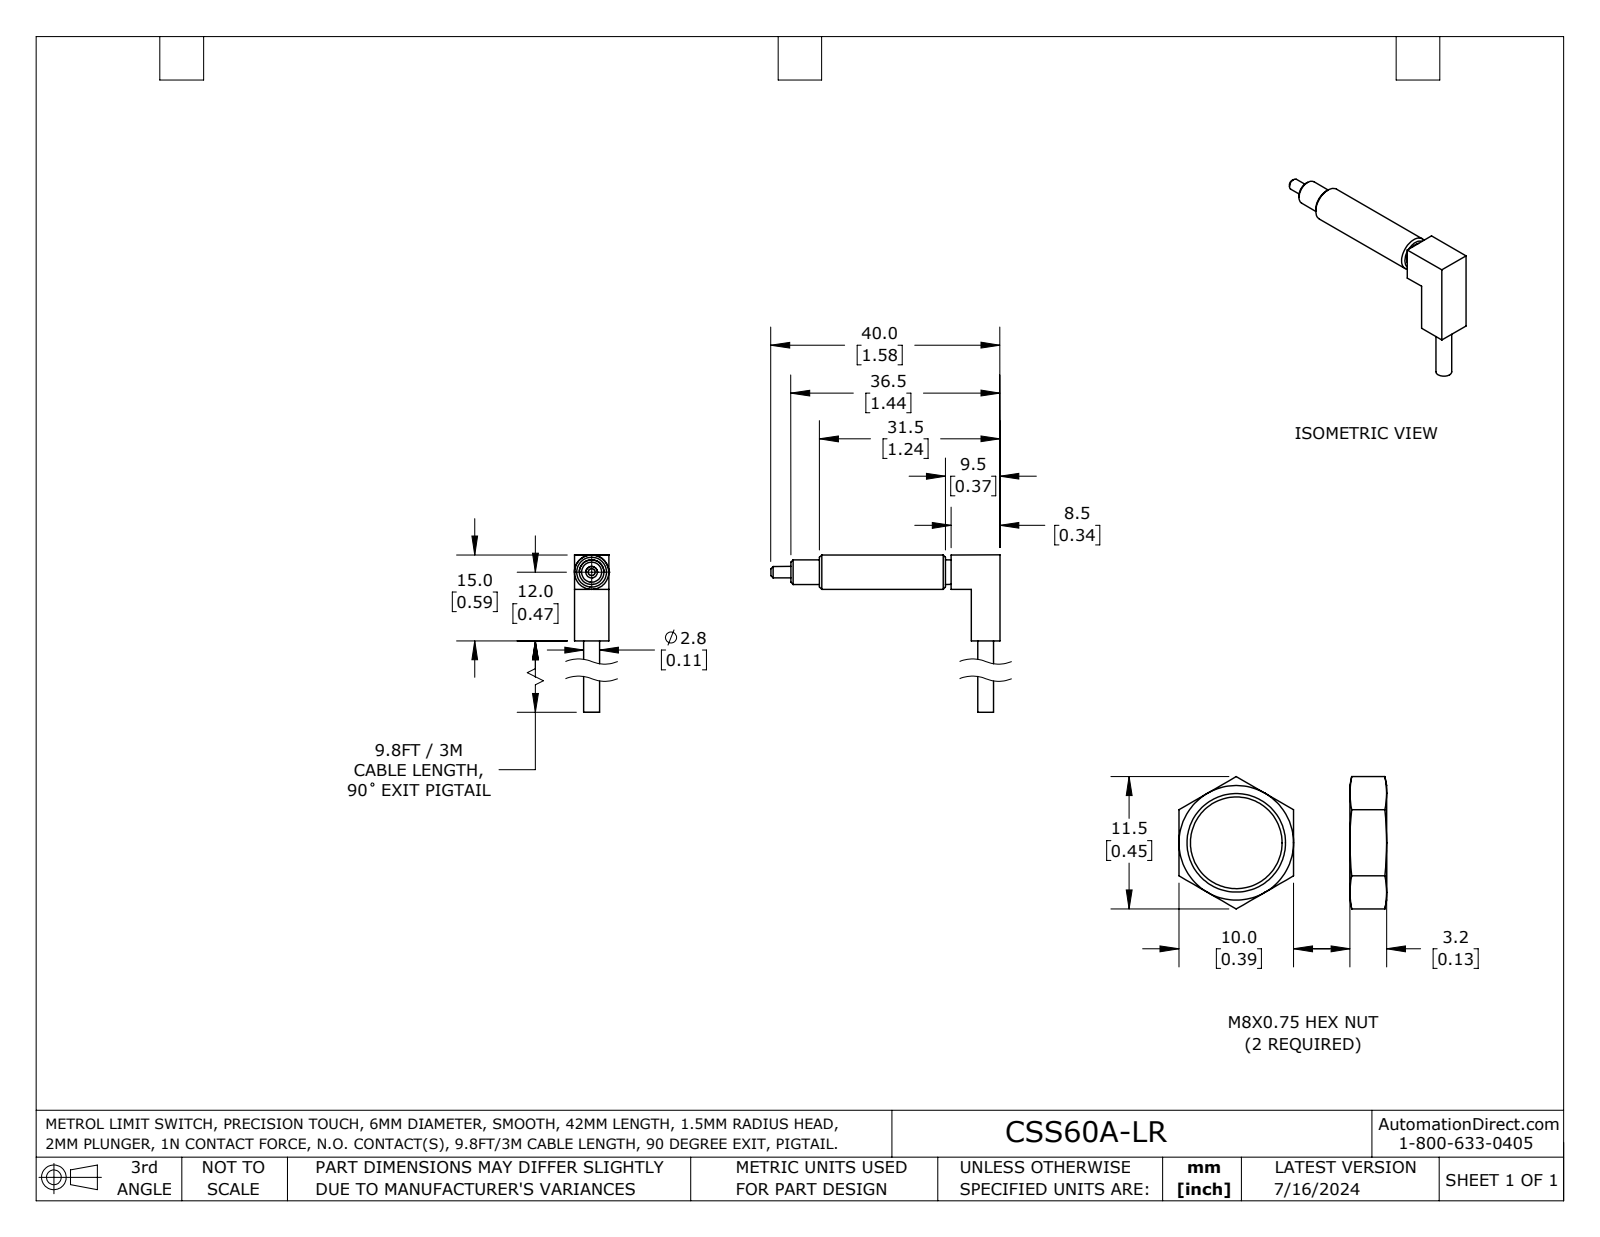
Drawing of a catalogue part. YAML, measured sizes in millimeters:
part_name: "CSS60A-LR"
step_written_by: "SolidWorks 2023 (AUTOMOTIVE_DESIGN)"
units: millimeters
bodies: {solids: 1, faces: 22, planar: 13, cylindrical: 5, other: 4}
overall_size: [40.02, 24.5, 6]
volume: 1350
surface_area: 1088
round_bosses_or_shafts:
  - {diameter: 6, count: 1}
  - {diameter: 4.3, count: 1}
  - {diameter: 2.77, count: 1}
  - {diameter: 2, count: 1}
face_to_face_distances: [6, 5, 15, 3.52, 8.52, 8.99, 6.01, 31.52, 23, 26.52]
